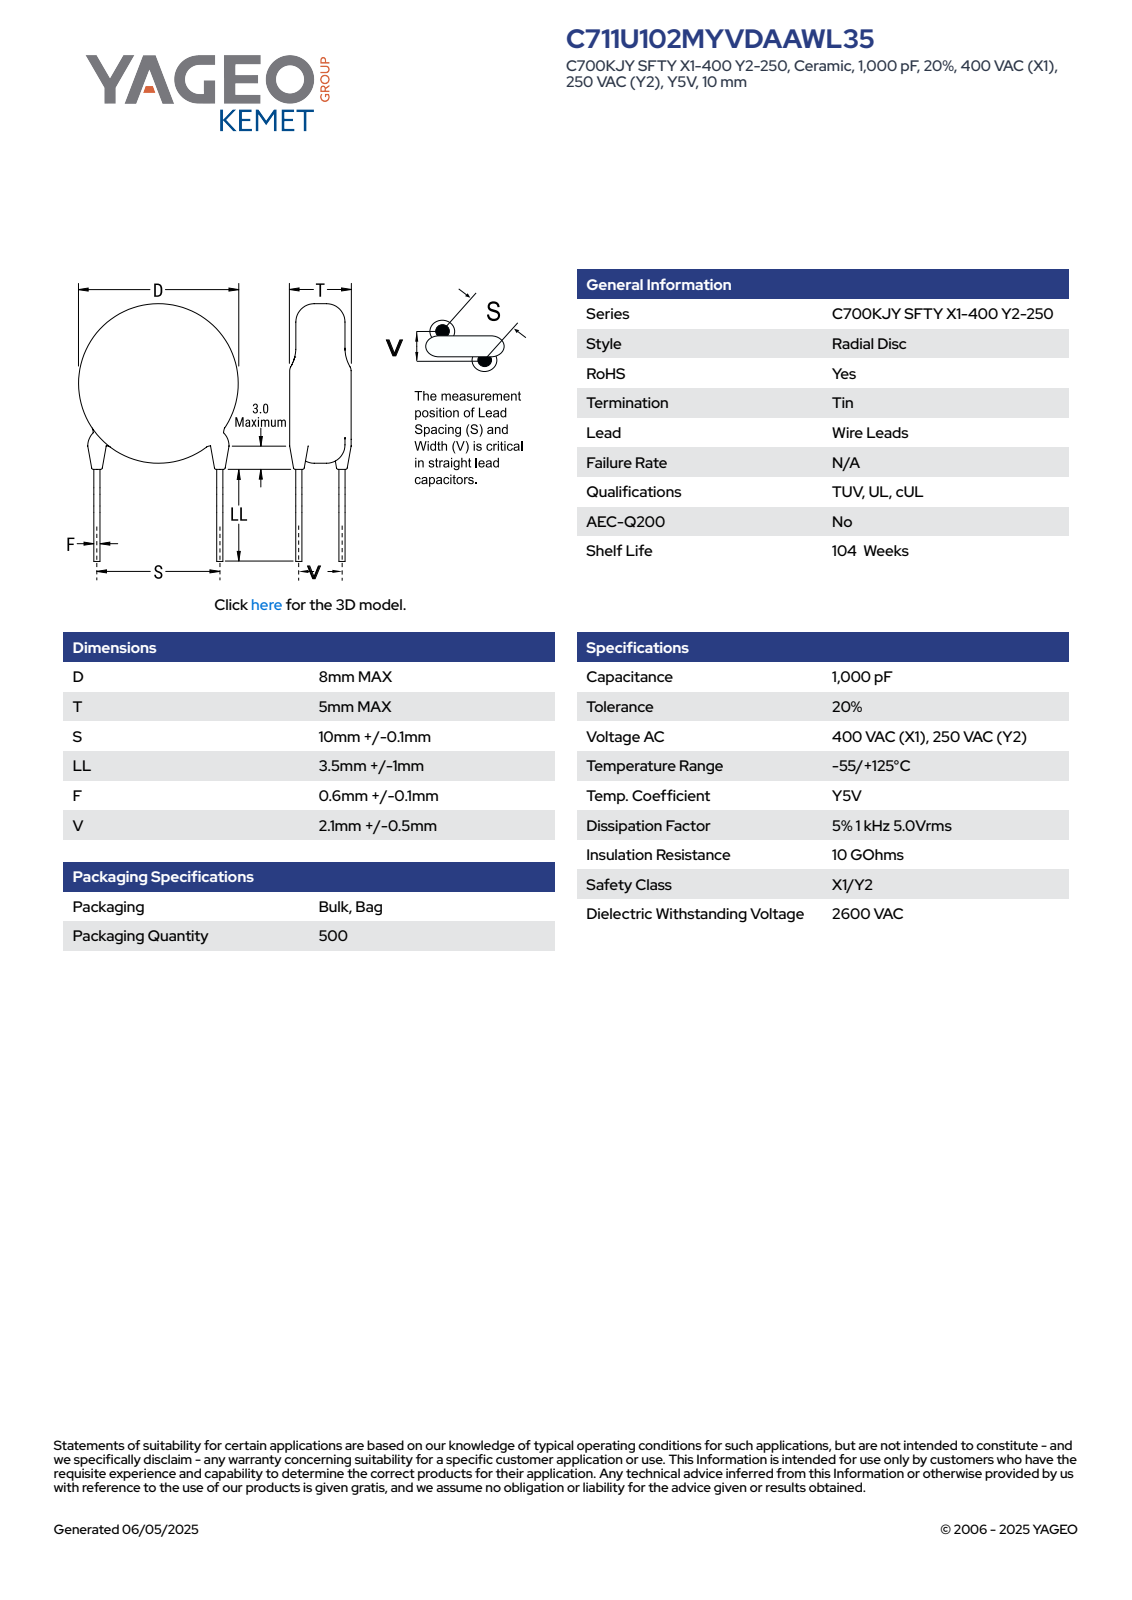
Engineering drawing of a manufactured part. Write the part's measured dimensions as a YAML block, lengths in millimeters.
part_name: "CCD_KST_8X5_D8T5S11LL4.5F0.7V2.1"
step_written_by: "SolidWorks 2021 (AUTOMOTIVE_DESIGN)"
units: millimeters
bodies: {solids: 4, faces: 81, planar: 63, cylindrical: 14, other: 4}
overall_size: [14, 11.2, 5]
volume: 255
surface_area: 264
round_bosses_or_shafts:
  - {diameter: 1.2, count: 4}
  - {diameter: 0.7, count: 2}
  - {diameter: 8, count: 1}
face_to_face_distances: [5, 4.5, 0.97, 10.52, 6.02, 9.55, 5.05, 0.36, 0.78, 3.96]
